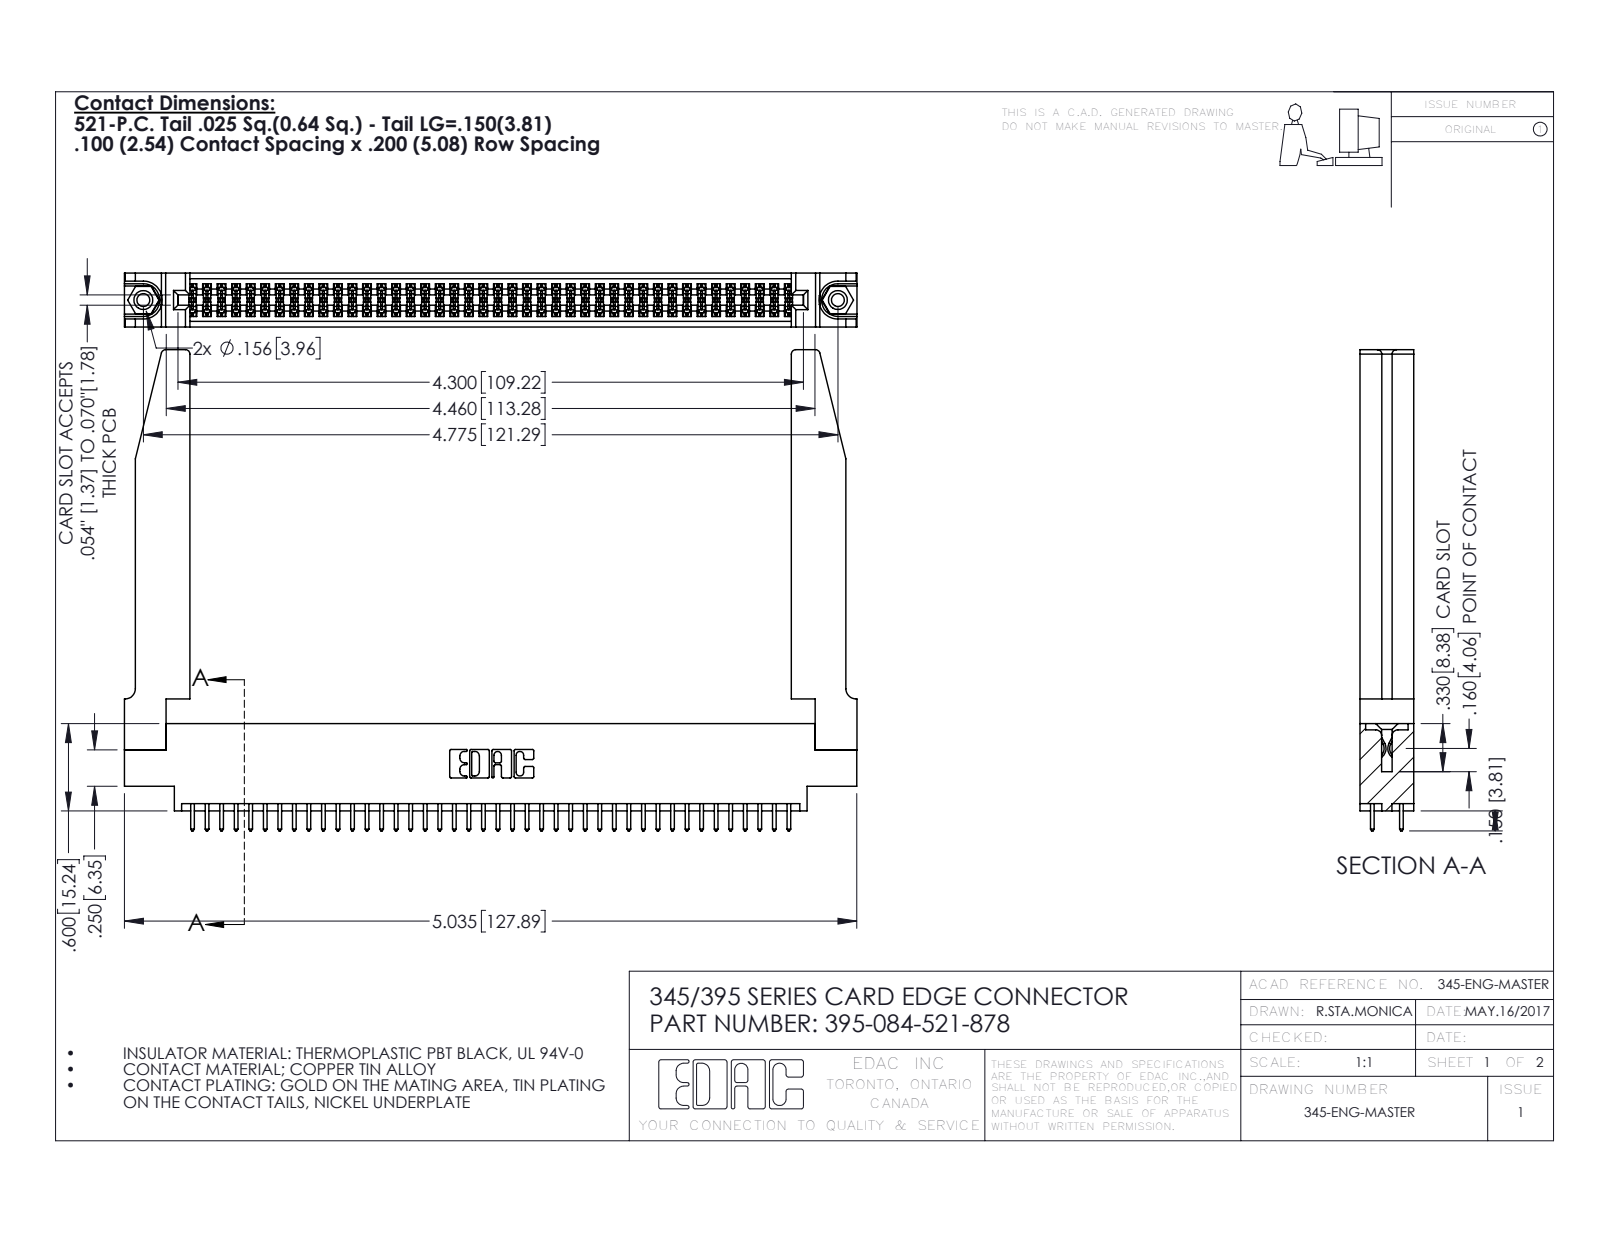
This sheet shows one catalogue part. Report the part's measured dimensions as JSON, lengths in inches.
{"part_name": "345-250-001_345-250-001-102; 345 Part_0.170 Offset - 0.156 Dia-TH; 395-084-521-878; 345-292-001_345-293-121 (+1 more)", "step_written_by": "SolidWorks 2016 (CONFIG_CONTROL_DESIGN)", "units": "inches", "bodies": {"solids": 89, "faces": 4564, "planar": 2998, "cylindrical": 1514, "other": 52}, "overall_size": [5.036, 3.307, 0.37], "volume_in3": 1.223, "surface_area_in2": 38.61, "round_holes": [[0.089, 2], [0.125, 2], [0.156, 2], [0.064, 1]], "round_bosses_or_shafts": [[0.155, 2]], "partial_cylinders_radius": [[0.006, 126], [0.01, 84], [0.01, 22], [0.03, 8], [0.007, 6], [0.031, 6], [0.026, 3], [0.014, 2]], "face_to_face_distances": [0.37, 0.072, 0.298, 0.098, 0.272, 0.025, 0.2, 0.225, 0.175, 0.148], "hole_center_spacings": [0.27, 4.539, 4.775]}
